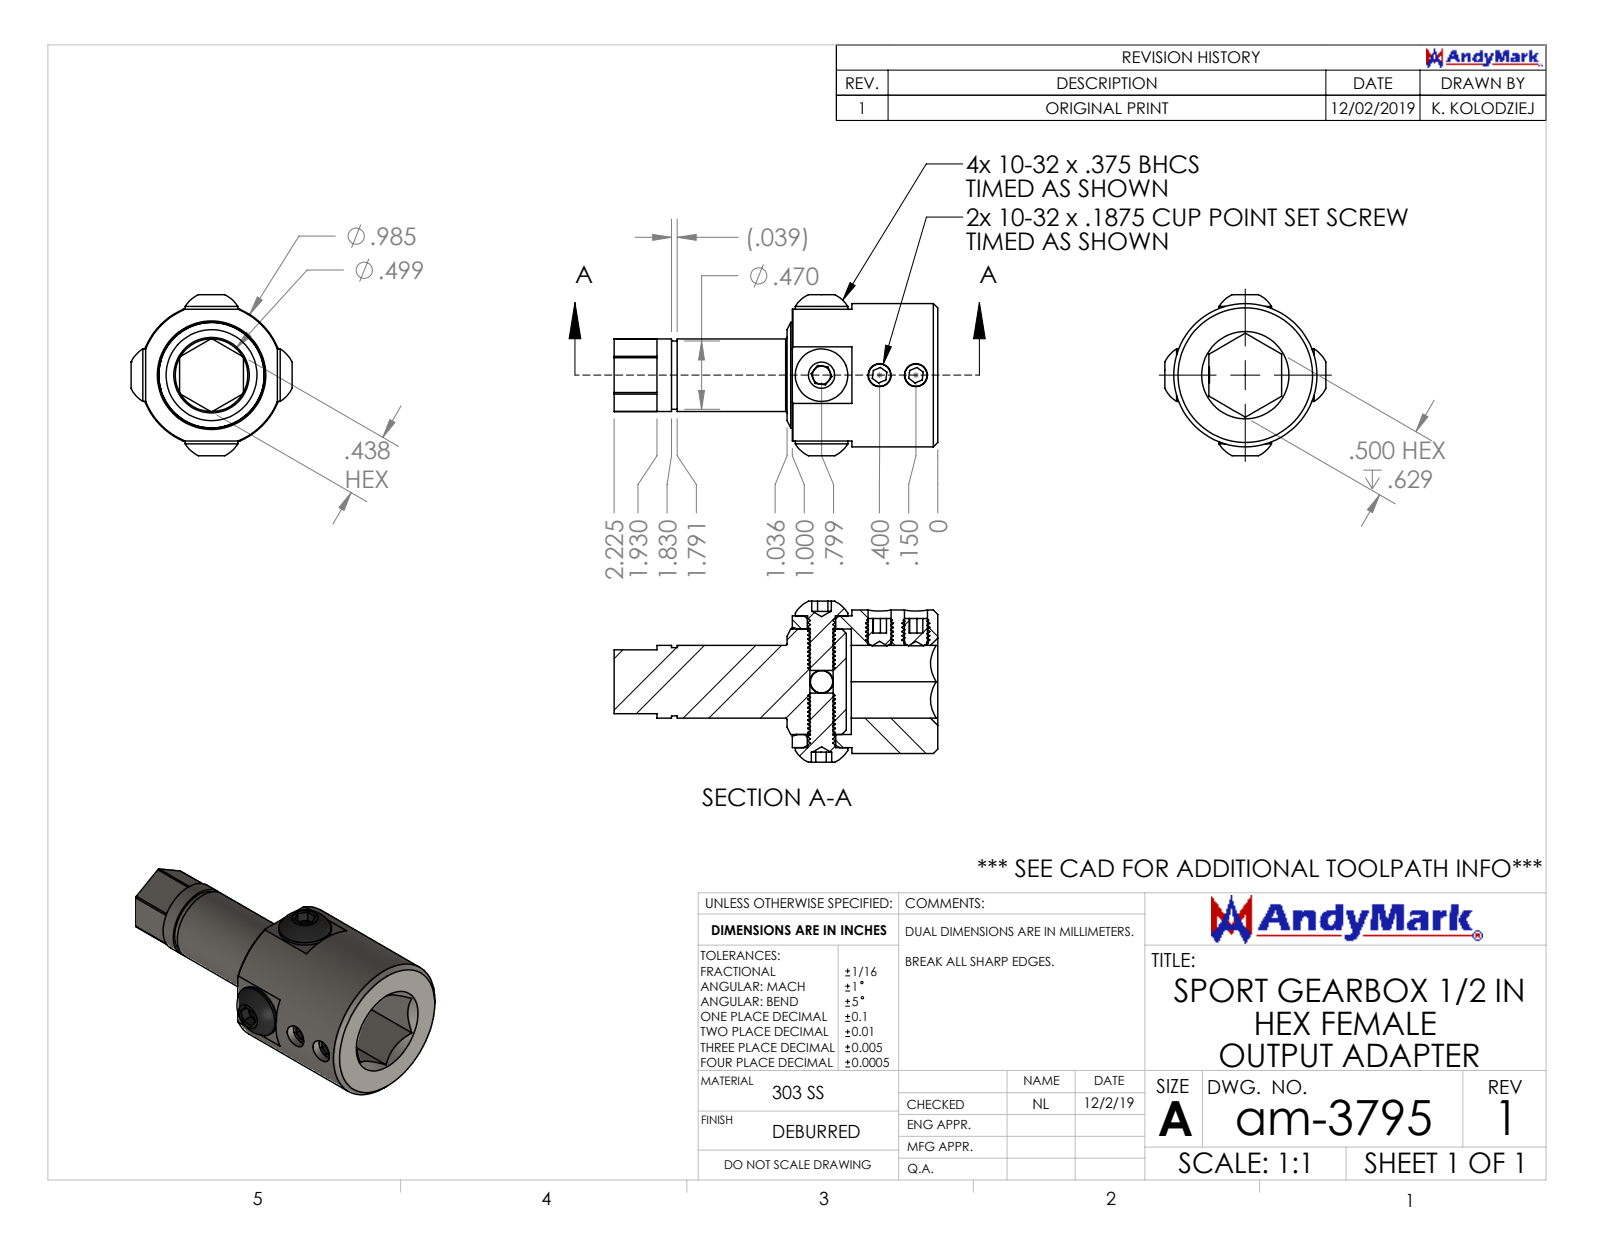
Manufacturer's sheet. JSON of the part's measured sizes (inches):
{"part_name": "socket button head cap screw_ai_SBHCSCREW 0.19-32x0.375-HX-S; socket set screw cup point_ai_SSCUPSKT 0.19-32x0.1875-HX-S; socket set screw cup point_ai; socket button head cap screw_ai (+3 more)", "step_written_by": "SolidWorks 2019 (AUTOMOTIVE_DESIGN)", "units": "inches", "bodies": {"solids": 8, "faces": 567, "planar": 111, "cylindrical": 156, "other": 300}, "overall_size": [2.225, 1.107, 1.107], "volume_in3": 0.854, "surface_area_in2": 13.13, "round_holes": [[0.159, 4], [0.196, 2], [0.726, 1]], "round_bosses_or_shafts": [[0.19, 4], [0.361, 2], [0.985, 1], [0.725, 1], [0.499, 1], [0.47, 1]], "face_to_face_distances": [0.5, 0.905, 0.629, 0.031, 0.469, 0.371, 1, 0.406, 0.035, 0.594], "hole_center_spacings": [0.25, 0.399, 0.649]}
